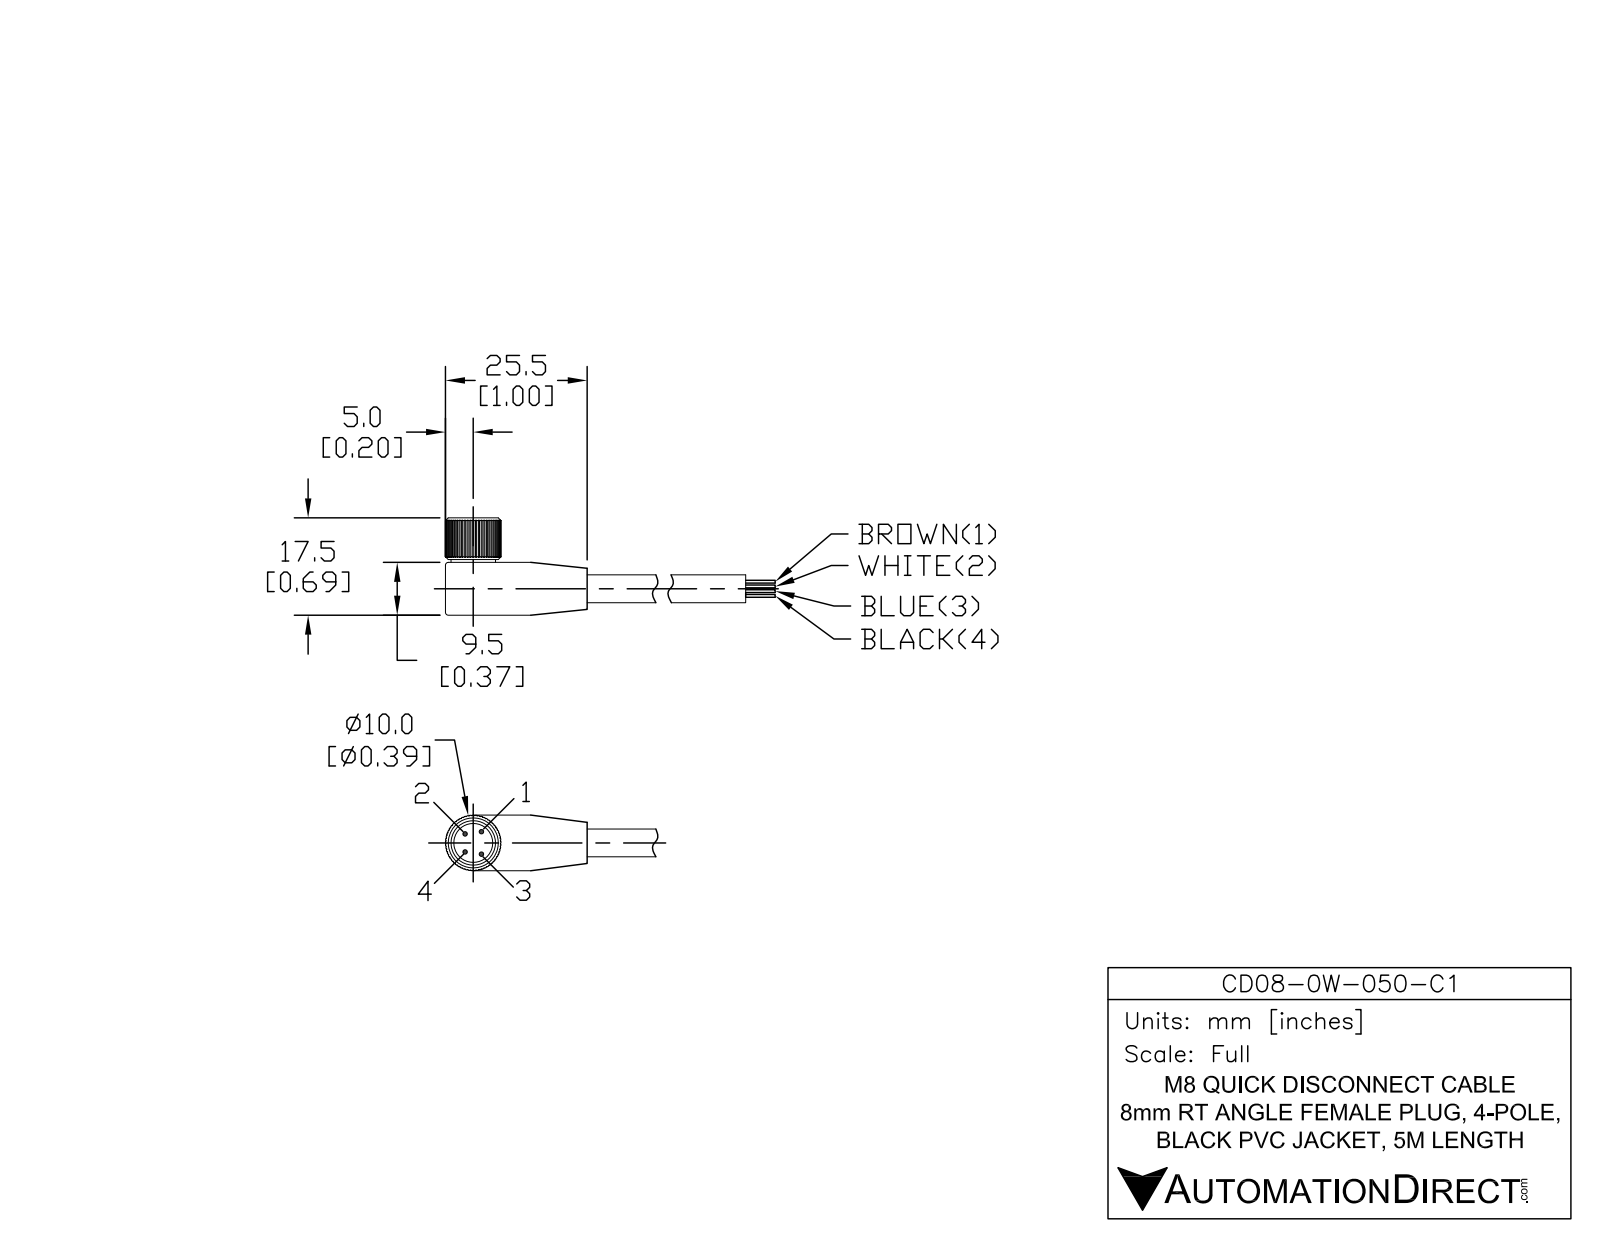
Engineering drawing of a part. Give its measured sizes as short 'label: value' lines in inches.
name: CD08-0W-050-C1
written by: SolidWorks 2017 (AUTOMOTIVE_DESIGN)
unit: in
bodies: 4 solids, 306 faces (220 planar, 83 cylindrical, 3 other)
size: 5.063 × 0.752 × 0.394
volume: 0.265 in³; area: 5.197 in²
holes: 4× ⌀0.035, 1× ⌀0.283, 1× ⌀0.315
bosses: 2× ⌀0.394, 1× ⌀0.276, 1× ⌀0.26, 1× ⌀0.189
rounds: 1× R0.193
face distances: 0.303, 0.024, 0.354, 0.28, 3.937, 0.181, 0.122, 0.157, 0.098, 0.205
hole spacings: 0.086, 0.098, 0.119, 0.185, 0.126, 0.157
